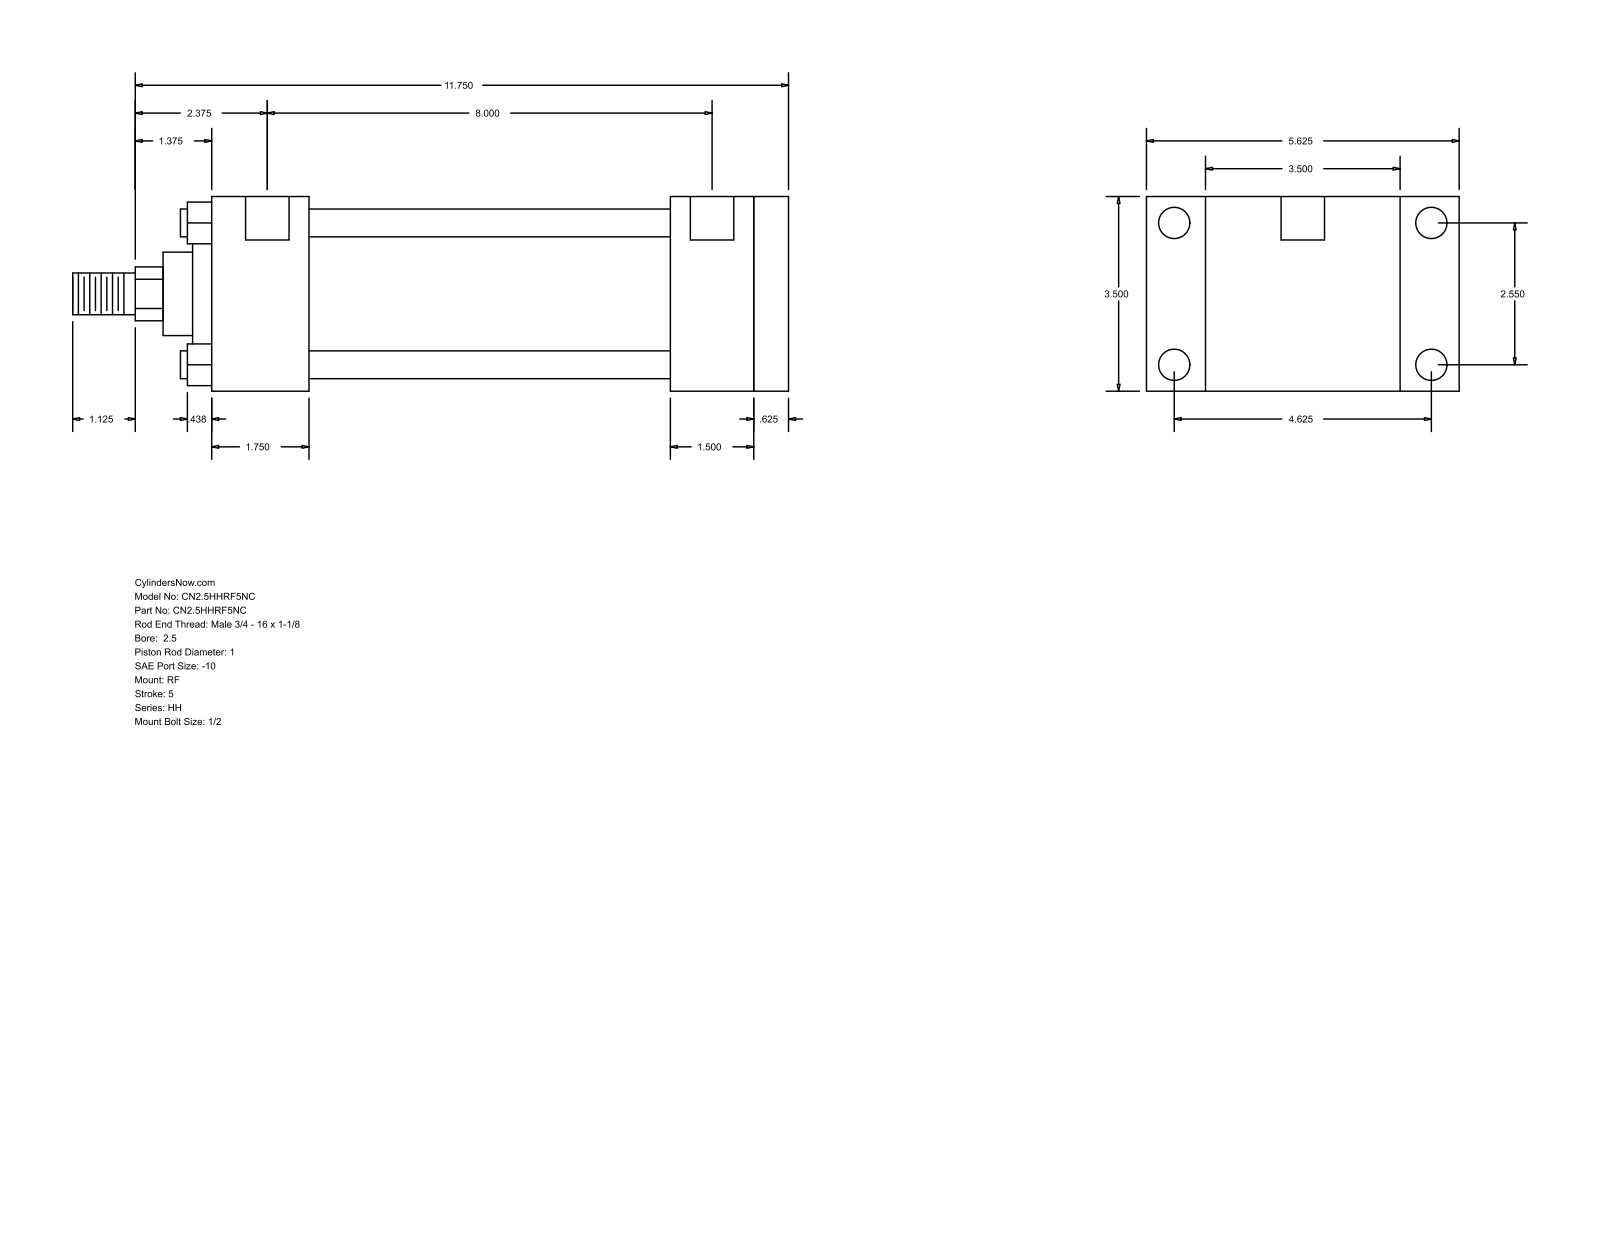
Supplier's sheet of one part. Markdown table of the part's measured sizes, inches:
| quantity | value |
| --- | --- |
| part name | HH_RF__0250_1 |
| STEP written by | GSSL Pune (CONFIG_CONTROL_DESIGN) |
| units | inches |
| bodies | 0 solids, 94 faces (65 planar, 29 cylindrical, 0 other) |
| overall size | 12.875 × 5.625 × 3.5 |
| round holes (diameter × count) | 0.219 × 4, 0.563 × 4, 0.781 × 2 |
| round bosses / shafts (diameter × count) | 0.5 × 4, 2.875 × 1, 2.375 × 1, 1.5 × 1, 1 × 1, 0.75 × 1 |
| partial cylindrical surfaces (radius × count) | 0.484 × 1 |
| main face-to-face distances | 3.5, 0.625, 9.75, 10.375, 1.5, 1.75, 8, 8.625, 8.25, 6.5 |
| hole center spacings | 0.063, 2.55, 4.625, 5.281, 8.062, 8.125, 8 |
